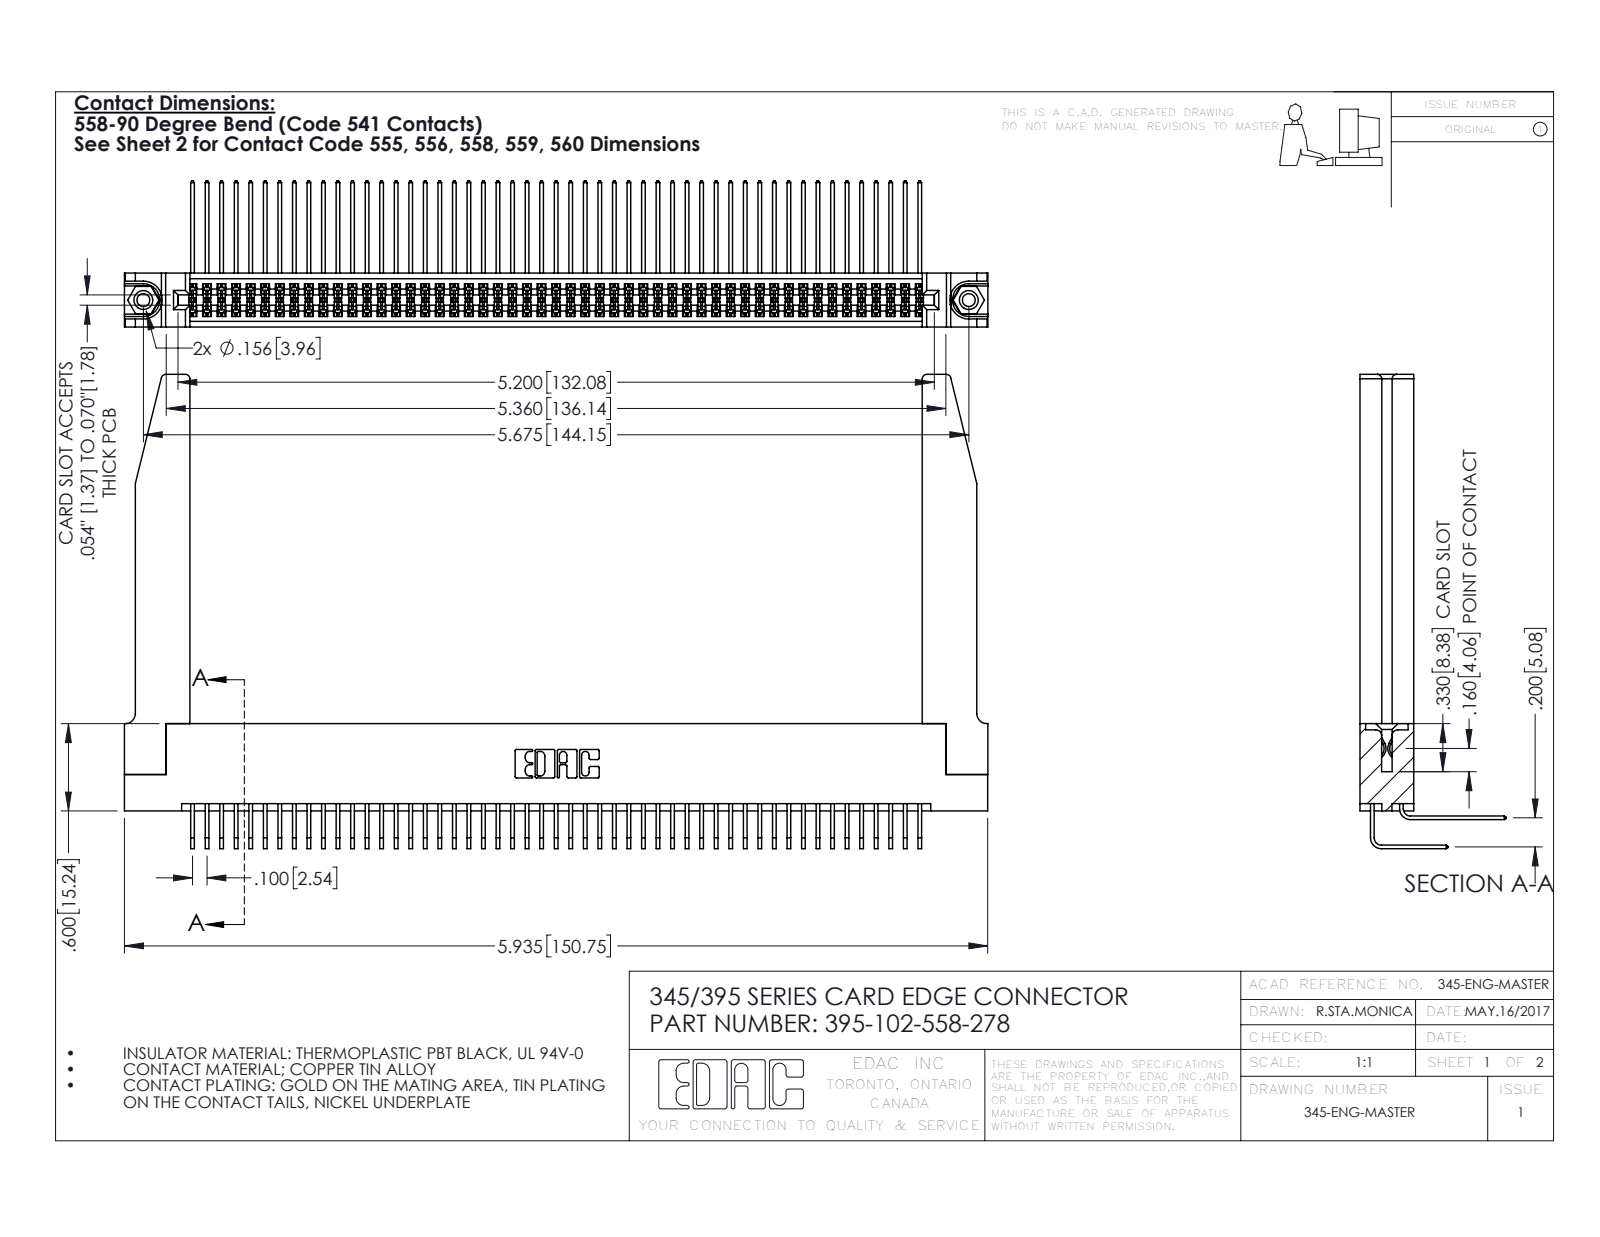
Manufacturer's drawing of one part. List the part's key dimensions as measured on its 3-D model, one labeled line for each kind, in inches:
Part name (STEP PRODUCT): 345-250-001_345-250-001-102; 345-292-001_558 Tail - 2; 395-102-558-278; 345-220-078_345-220-078 (+2 more)
STEP written by: SolidWorks 2016 (CONFIG_CONTROL_DESIGN)
Units: inches
Bodies: 107 solids, 5664 faces (3792 planar, 1820 cylindrical, 52 other)
Overall size (bounding box): 5.936 × 3.259 × 1.005
Volume: 1.409 in³ · Surface area: 50.26 in²
Round holes (diameter × count): ⌀0.089 ×2, ⌀0.125 ×2, ⌀0.156 ×2, ⌀0.064 ×1
Round bosses / shafts (diameter × count): ⌀0.155 ×2
Partial cylindrical surfaces — rounded edges, fillets, slot ends (radius × count): R0.006 ×154, R0.01 ×22, R0.03 ×8, R0.007 ×6, R0.031 ×6, R0.026 ×3, R0.014 ×2, R0.019 ×2
Main face-to-face distances: 0.072, 0.298, 0.37, 0.2, 0.098, 0.272, 0.025, 0.225, 0.285, 0.025
Hole centre spacings: 0.27, 5.439, 5.675
